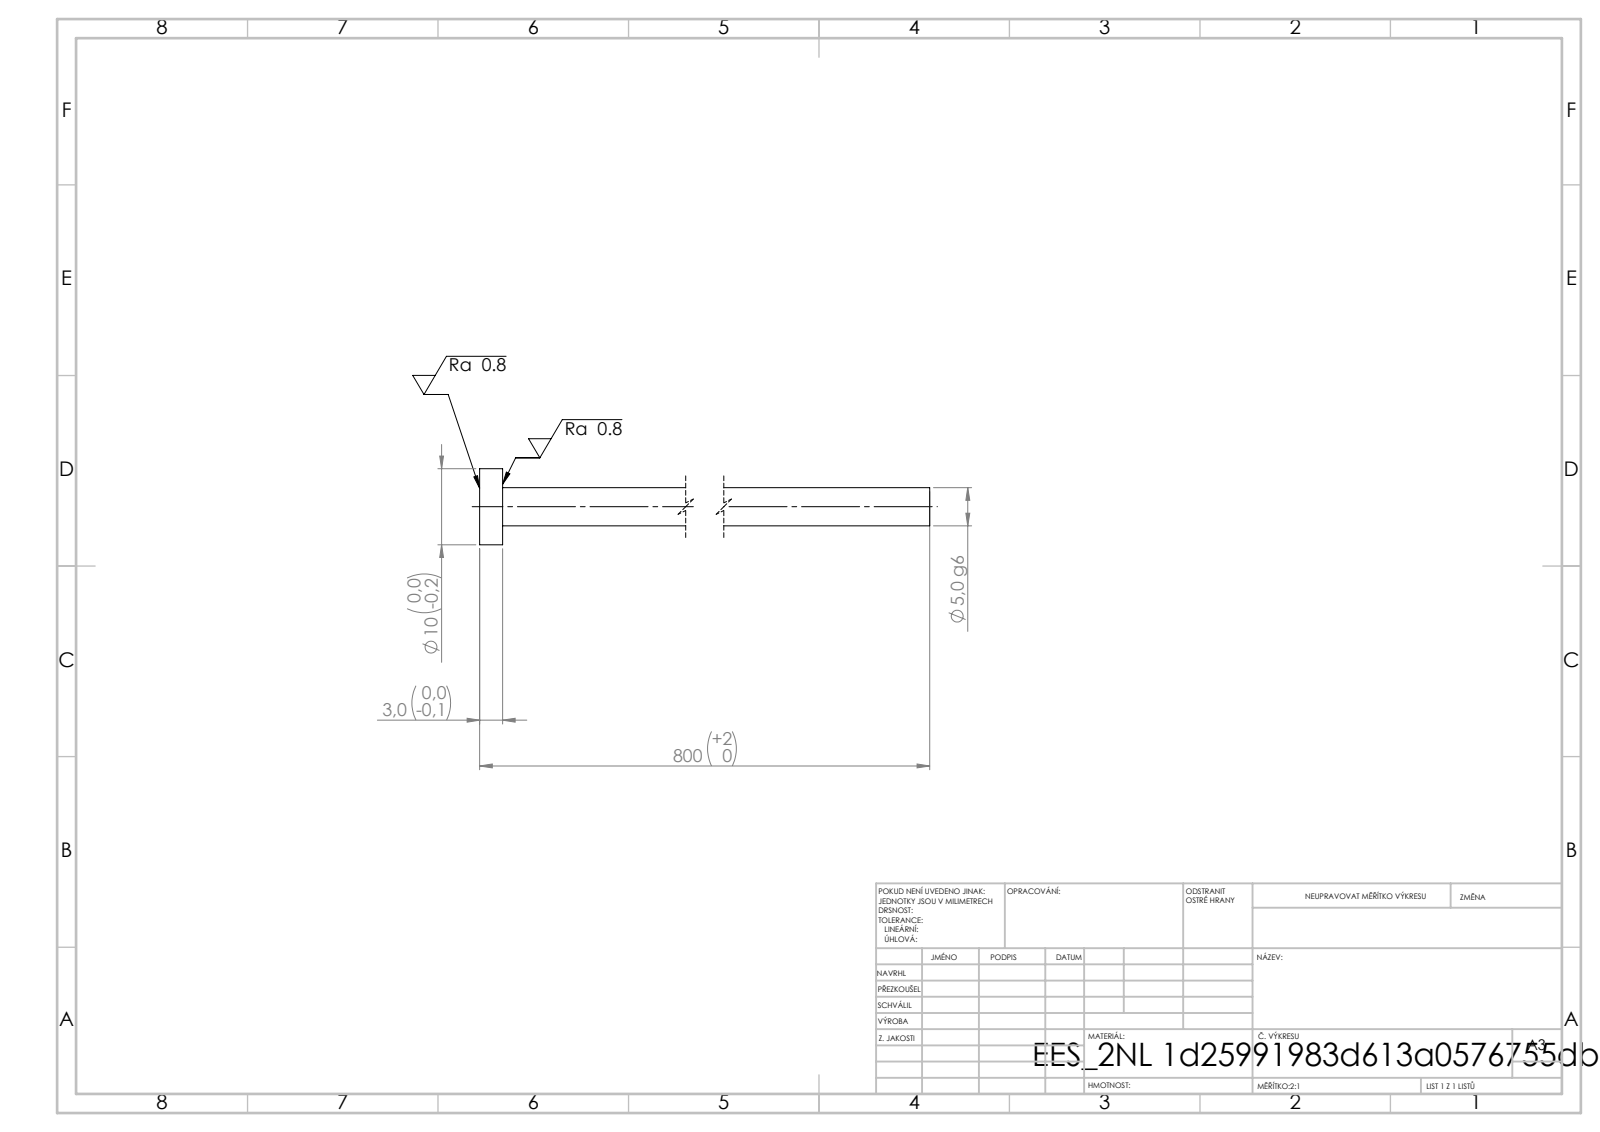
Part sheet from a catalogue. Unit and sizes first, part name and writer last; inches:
Units: inches
Overall size (bounding box): 31.496 × 0.394 × 0.394
Round bosses / shafts (diameter × count): ⌀0.394 ×1, ⌀0.197 ×1
Main face-to-face distances: 0.118, 31.496, 31.378
Volume: 0.969 in³ · Surface area: 19.8 in²
Bodies: 1 solid, 7 faces (3 planar, 4 cylindrical, 0 other)
STEP written by: SolidWorks 2019 (CONFIG_CONTROL_DESIGN)
